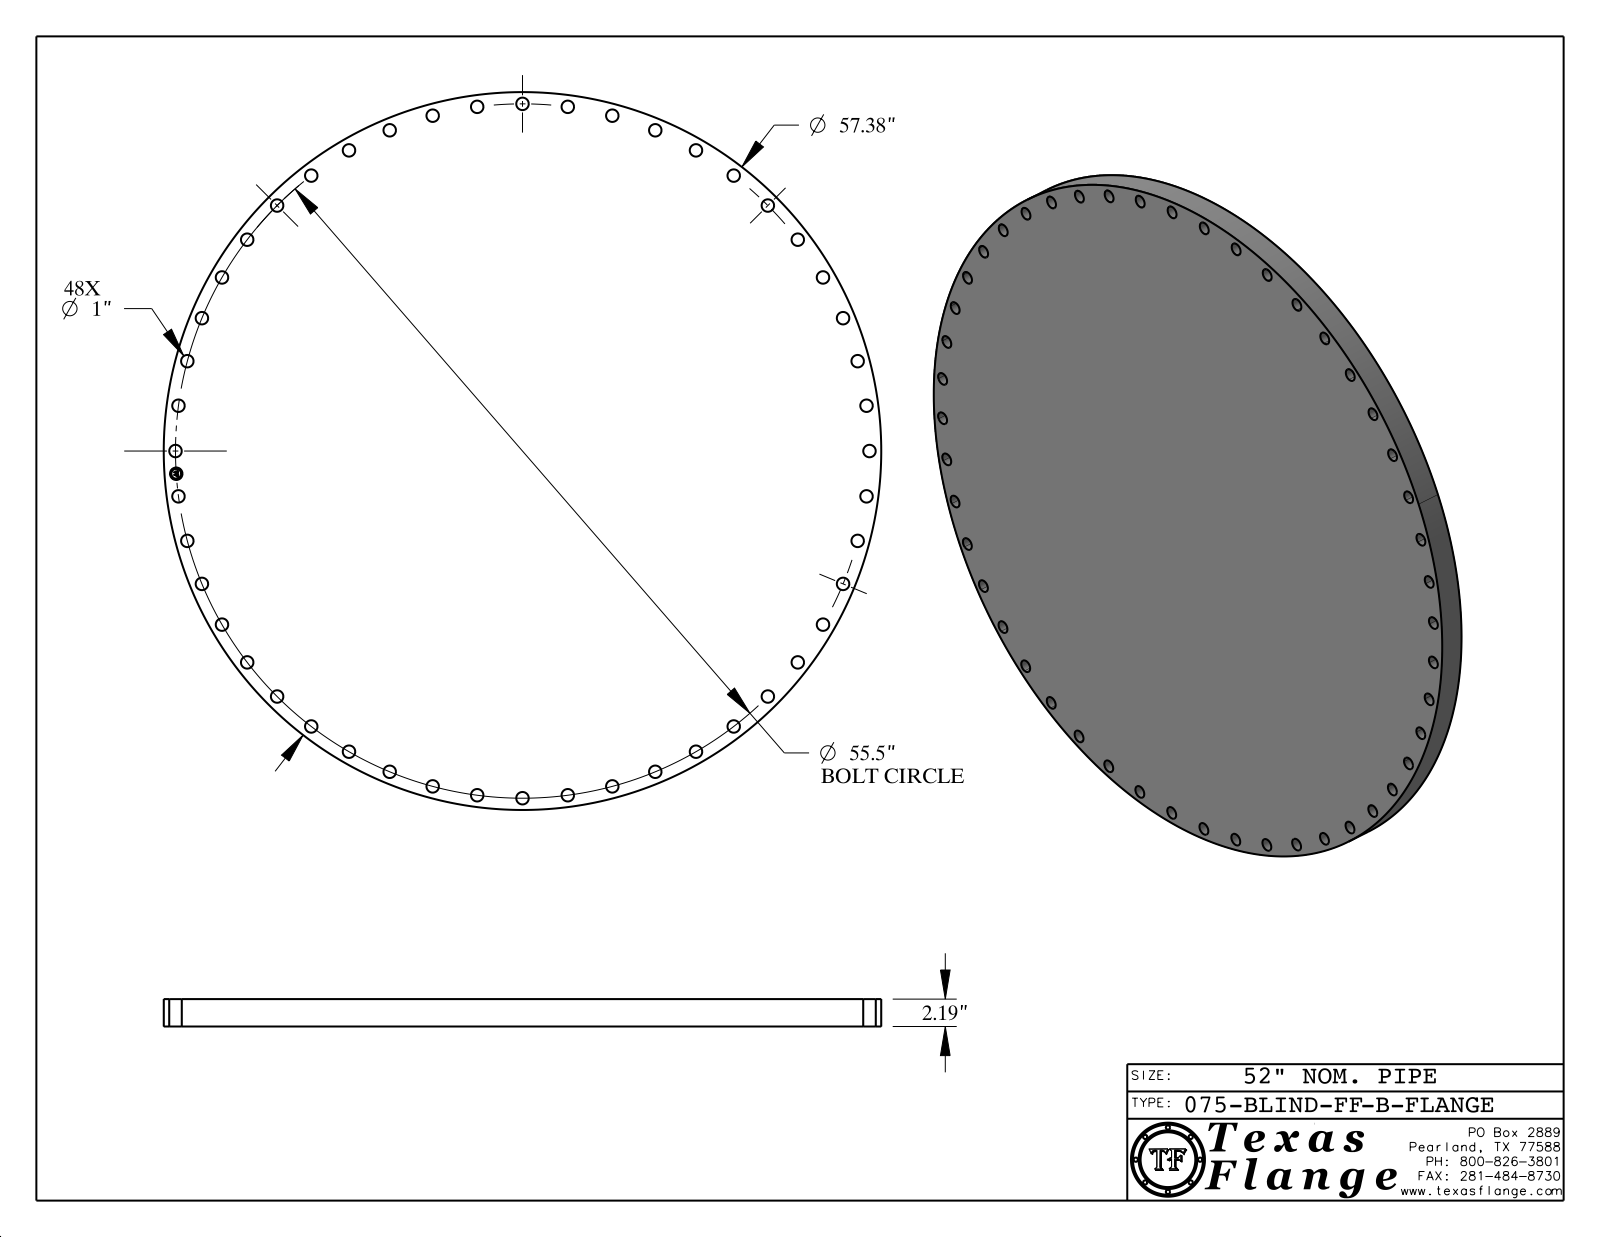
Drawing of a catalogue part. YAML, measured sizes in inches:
part_name: "075-BLIND-FF, Series B"
step_written_by: "CATIA V5 STEP AP214 (AUTOMOTIVE_DESIGN)"
units: inches
bodies: {solids: 1, faces: 485, planar: 367, cylindrical: 118, other: 0}
overall_size: [57.38, 57.38, 2.19]
volume: 5581
surface_area: 5822
round_holes:
  - {diameter: 1, count: 49}
round_bosses_or_shafts:
  - {diameter: 0.061, count: 8}
  - {diameter: 57.38, count: 1}
  - {diameter: 0.788, count: 1}
face_to_face_distances: [2.19, 2.175, 0.015, 0.298, 0.293, 0.054, 0.193, 0.248, 0.044, 0.15]
hole_center_spacings: [7.244, 55.025, 55.381, 10.828, 3.63, 52.555, 54.434, 53.609]
